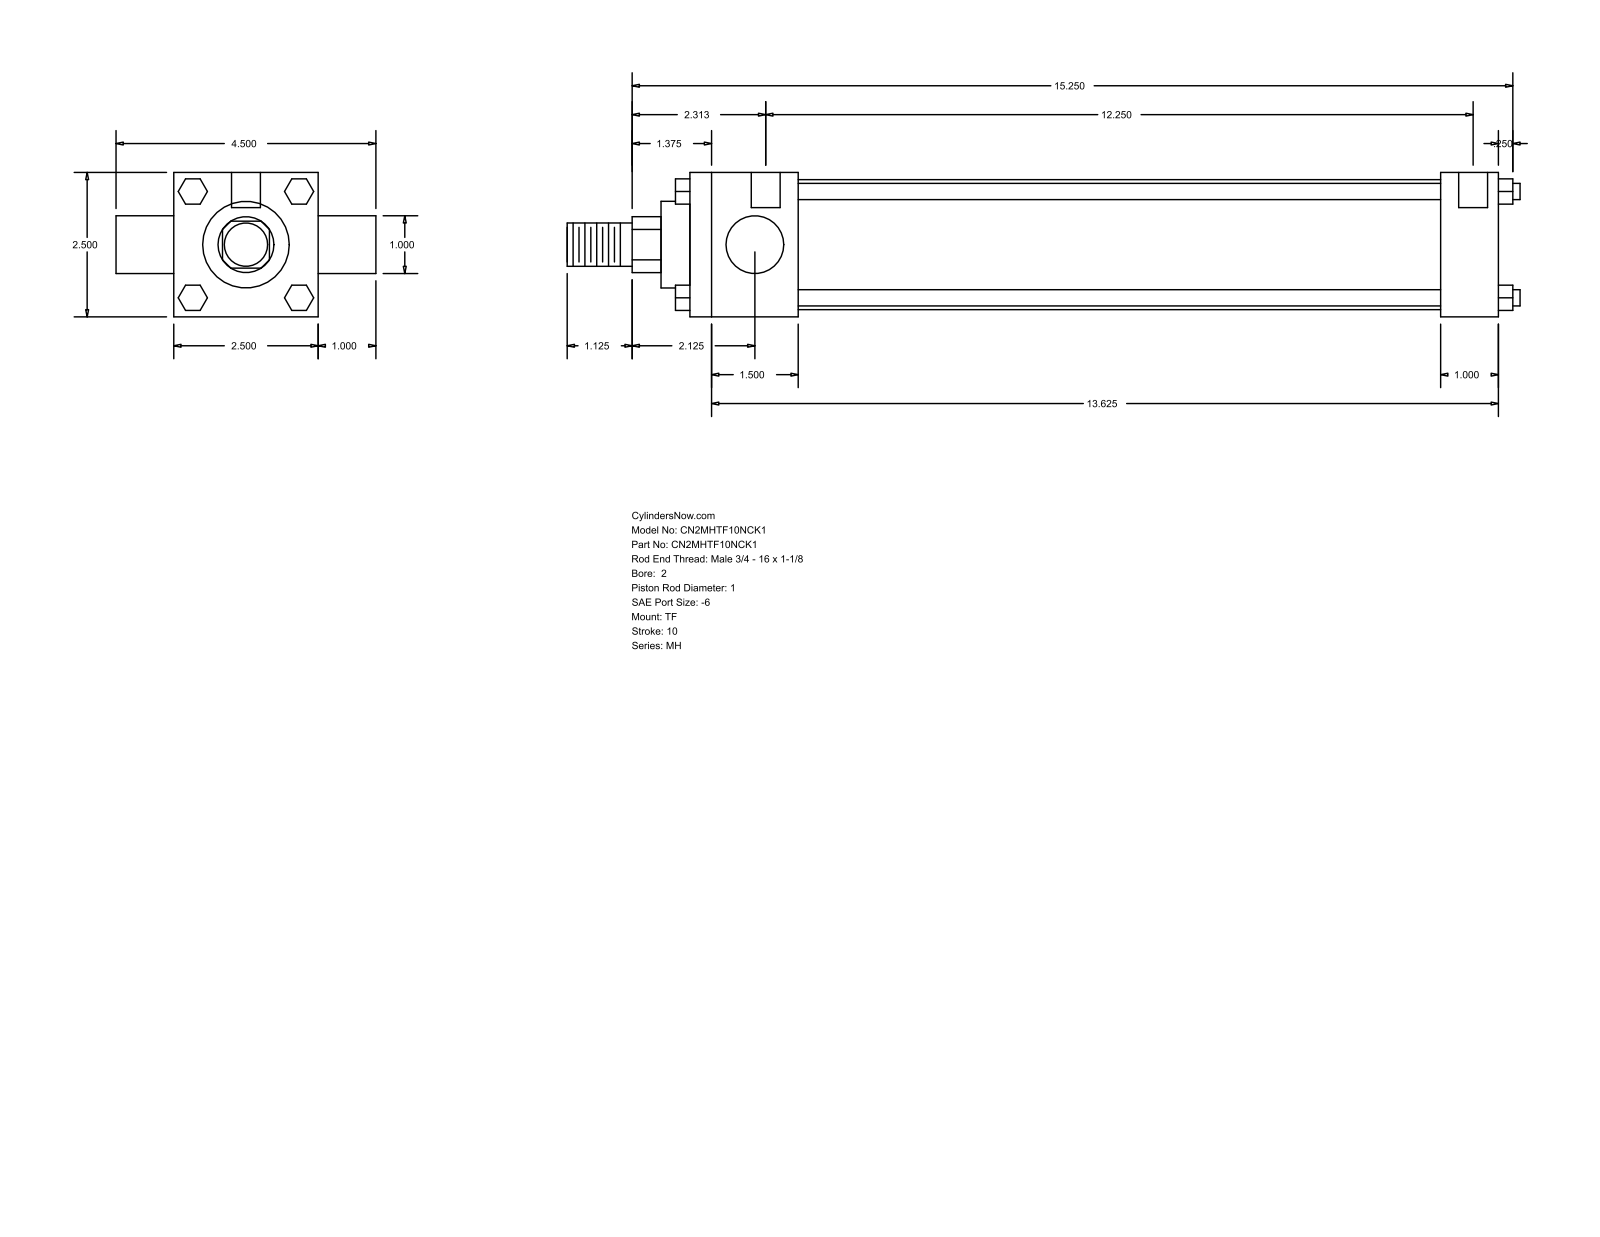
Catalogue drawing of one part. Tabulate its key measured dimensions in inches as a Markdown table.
| quantity | value |
| --- | --- |
| part name | MH_TF__0200_1 |
| STEP written by | GSSL Pune (CONFIG_CONTROL_DESIGN) |
| units | inches |
| bodies | 0 solids, 120 faces (92 planar, 28 cylindrical, 0 other) |
| overall size | 16.5 × 4.5 × 2.5 |
| round holes (diameter × count) | 0.219 × 3, 0.5 × 2 |
| round bosses / shafts (diameter × count) | 0.281 × 4, 1 × 2, 2.25 × 1, 1.5 × 1, 0.75 × 1 |
| partial cylindrical surfaces (radius × count) | 0.484 × 1 |
| main face-to-face distances | 2.5, 14, 1, 1.875, 13, 11.125, 12.125, 3.5, 14.5, 0.25 |
| hole center spacings | 0.125, 0.187, 12.25, 12.375, 12.437, 12.562 |
